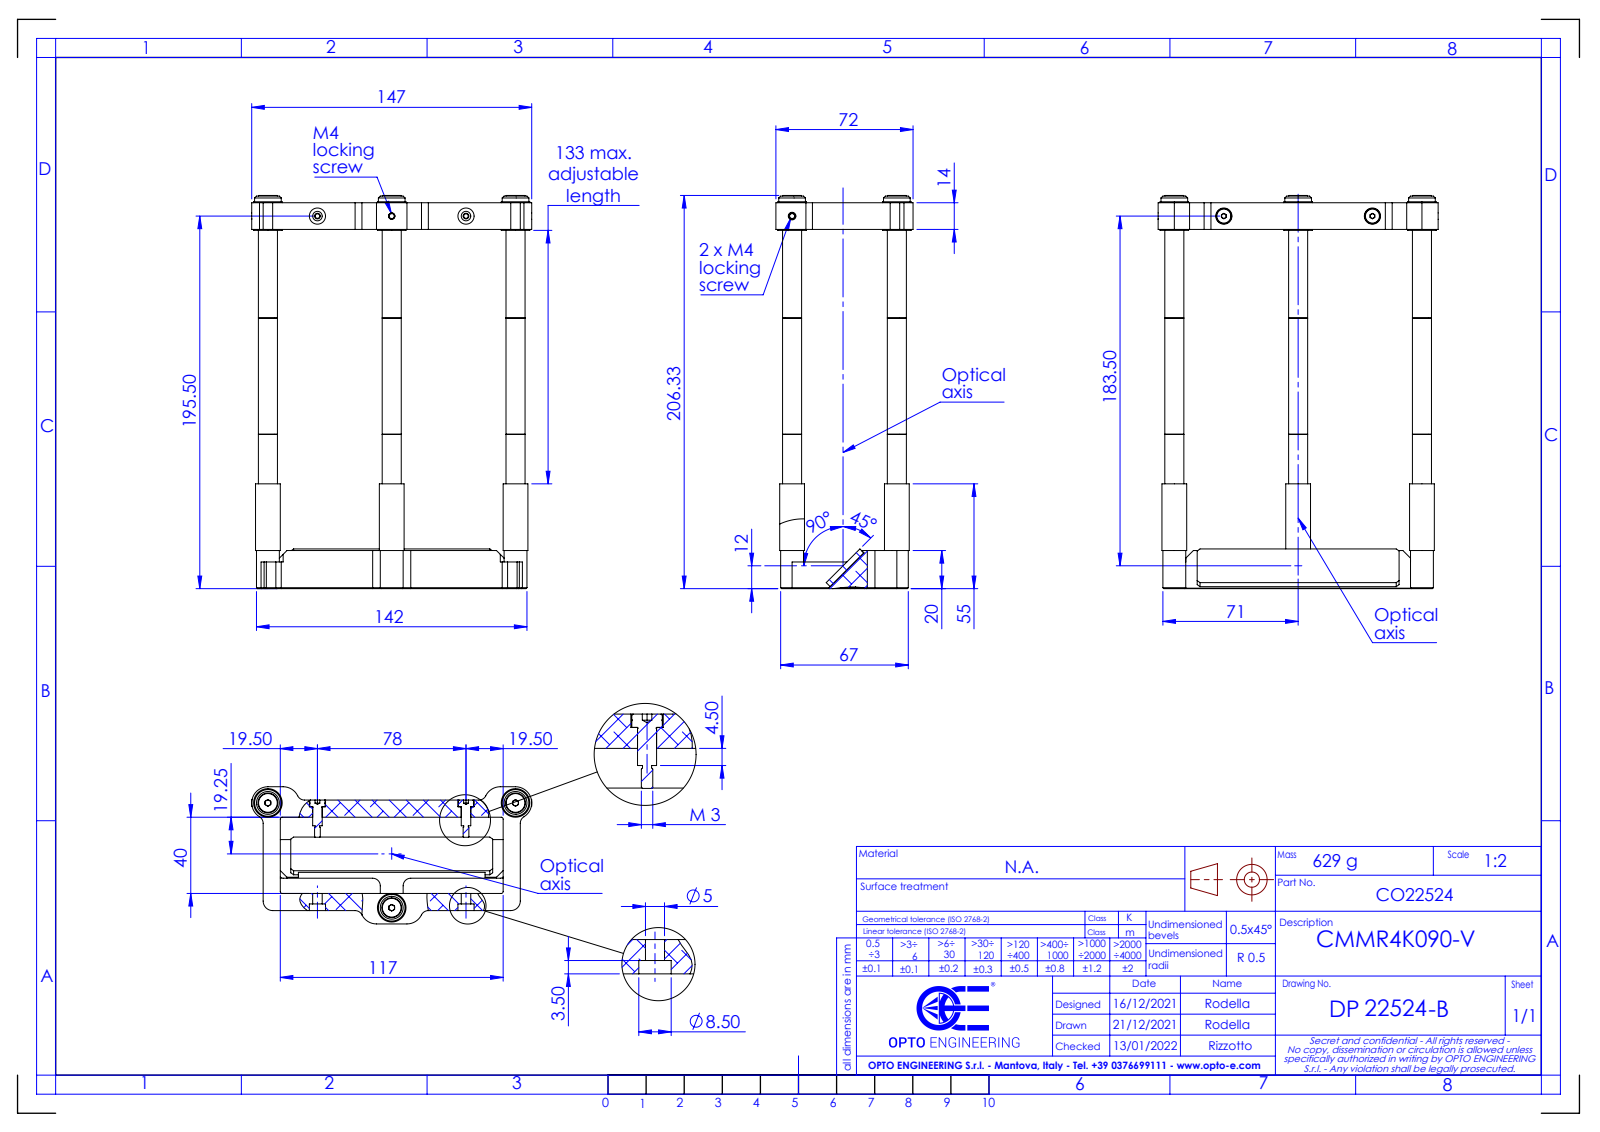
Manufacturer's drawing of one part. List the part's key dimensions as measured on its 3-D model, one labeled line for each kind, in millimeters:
Part name (STEP PRODUCT): DP22524-B_CMMR4K090-V
STEP written by: SolidWorks 2021 (CONFIG_CONTROL_DESIGN)
Units: millimetres
Bodies: 0 solids, 282 faces (133 planar, 109 cylindrical, 40 other)
Overall size (bounding box): 206.32 × 147 × 72
Round holes (diameter × count): ⌀5 ×2, ⌀8.5 ×2
Round bosses / shafts (diameter × count): ⌀15 ×3, ⌀14 ×3, ⌀13 ×3, ⌀10 ×3, ⌀9.85 ×3, ⌀12 ×2, ⌀8 ×2, ⌀3 ×2
Partial cylindrical surfaces — rounded edges, fillets, slot ends (radius × count): R4 ×14, R8.5 ×6, R1 ×4, R2 ×2, R5 ×2, R6 ×1
Main face-to-face distances: 14, 188.5, 9, 202.5, 3, 49, 8, 0.5, 126, 40
Hole centre spacings: 78
